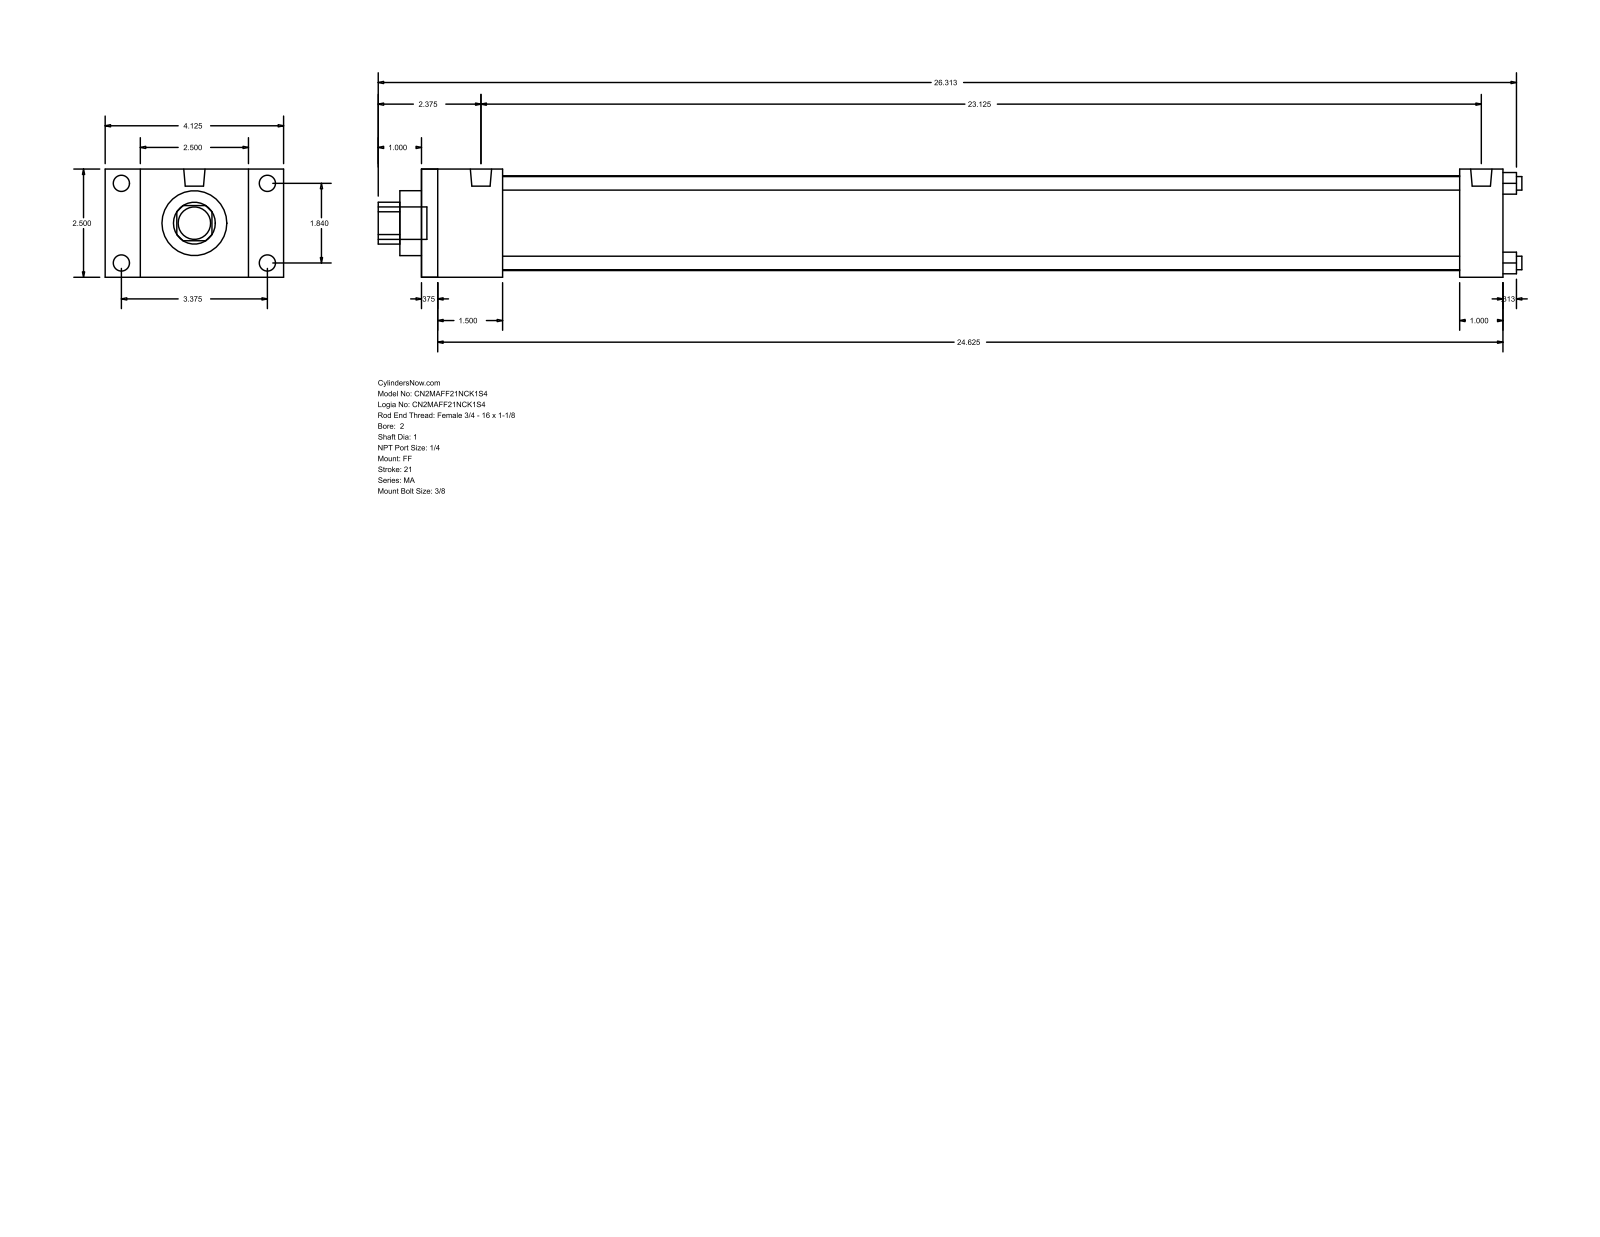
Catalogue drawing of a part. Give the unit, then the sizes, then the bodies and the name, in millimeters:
Units: millimetres
Overall size (bounding box): 671.51 × 104.78 × 63.5
Round holes (diameter × count): ⌀7.94 ×4, ⌀25.4 ×1, ⌀38.1 ×1, ⌀55.63 ×1
Round bosses / shafts (diameter × count): ⌀9.53 ×4, ⌀7.94 ×4, ⌀12.49 ×2, ⌀19.05 ×1
Partial cylindrical surfaces — rounded edges, fillets, slot ends (radius × count): R12.29 ×1
Main face-to-face distances: 63.5, 635, 9.52, 625.48, 25.4, 20.64, 12.7, 47.63, 609.6, 38.11
Hole centre spacings: 33.05, 46.74, 66.1
Bodies: 0 solids, 92 faces (64 planar, 28 cylindrical, 0 other)
Part name (STEP PRODUCT): MA_FF__0200_1
STEP written by: GSSL Pune (CONFIG_CONTROL_DESIGN)
